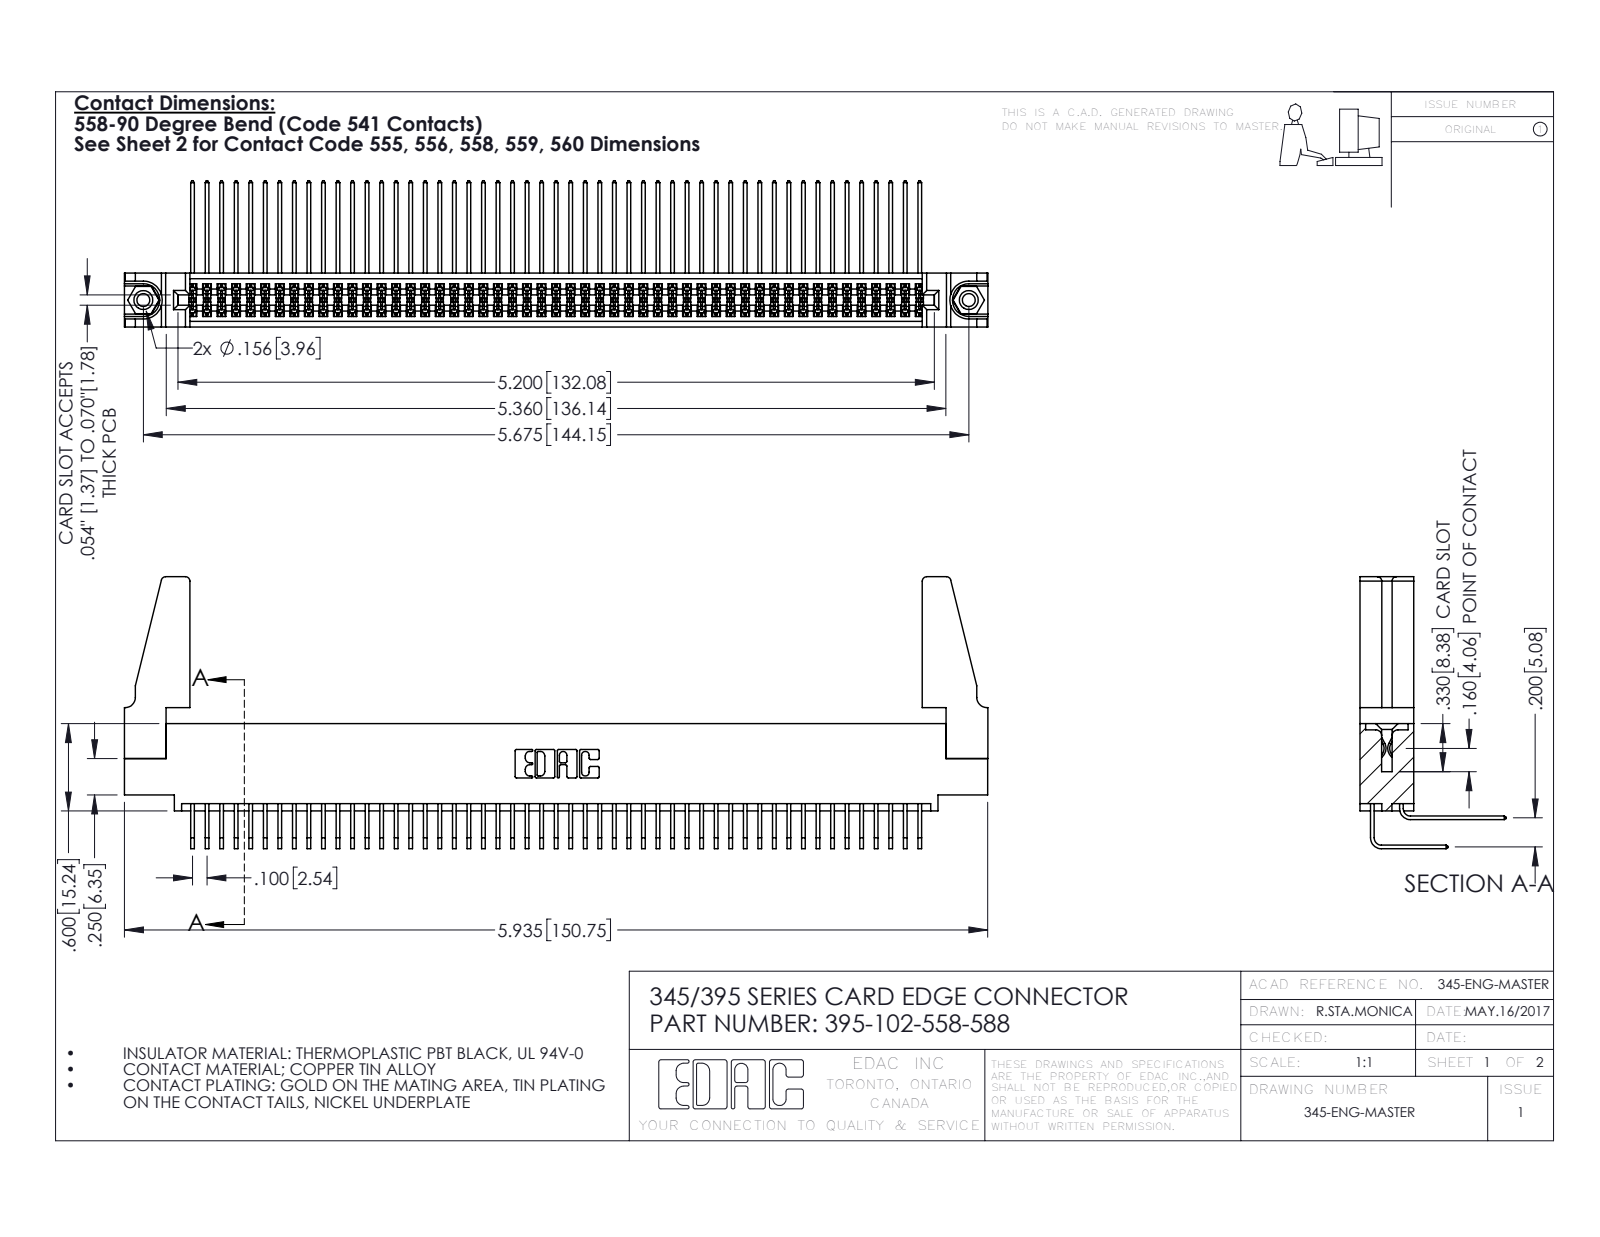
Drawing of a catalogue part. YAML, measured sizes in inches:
part_name: "345-220-078_345-220-088; 345 Part_0.110 Offset - 0.156 Dia-TH; 395-102-558-588; 345-292-001_558 Tail - 2 (+2 more)"
step_written_by: "SolidWorks 2016 (CONFIG_CONTROL_DESIGN)"
units: inches
bodies: {solids: 107, faces: 5558, planar: 3726, cylindrical: 1816, other: 16}
overall_size: [5.936, 1.869, 1.005]
volume: 1.129
surface_area: 44.47
round_holes:
  - {diameter: 0.089, count: 2}
  - {diameter: 0.125, count: 2}
  - {diameter: 0.156, count: 2}
  - {diameter: 0.064, count: 1}
round_bosses_or_shafts:
  - {diameter: 0.155, count: 2}
partial_cylinders:
  - {radius: 0.006, count: 154}
  - {radius: 0.01, count: 22}
  - {radius: 0.03, count: 8}
  - {radius: 0.007, count: 6}
  - {radius: 0.031, count: 6}
  - {radius: 0.026, count: 3}
  - {radius: 0.014, count: 2}
  - {radius: 0.019, count: 2}
face_to_face_distances: [0.072, 0.298, 0.2, 0.37, 0.098, 0.272, 0.025, 0.225, 0.025, 0.175]
hole_center_spacings: [0.27, 5.439, 5.675]
